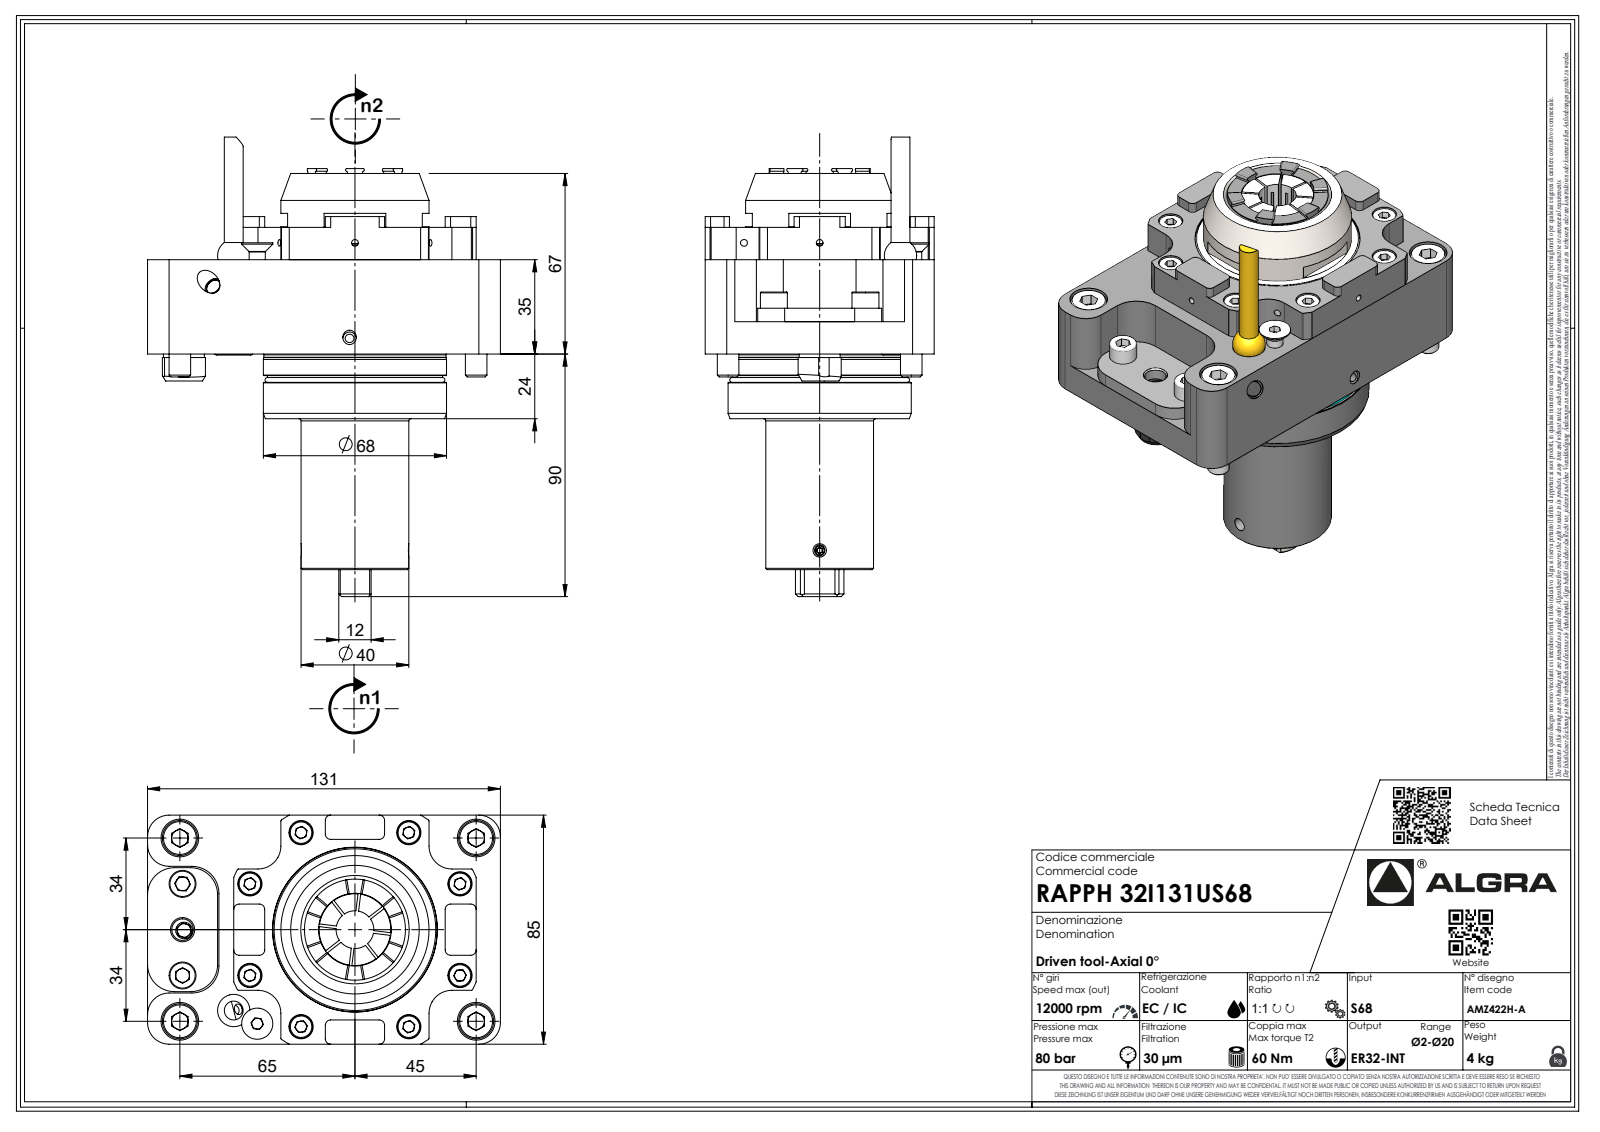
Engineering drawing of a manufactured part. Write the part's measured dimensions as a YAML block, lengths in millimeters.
part_name: "RAPPH32I131US68"
step_written_by: "SolidWorks 2023 (AUTOMOTIVE_DESIGN)"
units: millimeters
bodies: {solids: 8, faces: 716, planar: 354, cylindrical: 132, other: 230}
overall_size: [170.5, 131, 85]
volume: 668975
surface_area: 73592
round_holes:
  - {diameter: 2.1, count: 1}
  - {diameter: 4, count: 1}
  - {diameter: 5, count: 1}
  - {diameter: 27, count: 1}
  - {diameter: 33.45, count: 1}
round_bosses_or_shafts:
  - {diameter: 6, count: 3}
  - {diameter: 10, count: 2}
  - {diameter: 68, count: 1}
  - {diameter: 65, count: 1}
  - {diameter: 55, count: 1}
  - {diameter: 40, count: 1}
  - {diameter: 37.5, count: 1}
  - {diameter: 21.5, count: 1}
partial_cylinders:
  - {radius: 2, count: 17}
  - {radius: 0.5, count: 8}
  - {radius: 0.33, count: 7}
  - {radius: 0.52, count: 7}
  - {radius: 3.7, count: 7}
  - {radius: 8, count: 6}
  - {radius: 10, count: 6}
  - {radius: 8.5, count: 4}
face_to_face_distances: [35, 12, 85, 47, 24, 20, 59, 17, 32, 71]
hole_center_spacings: [26]
